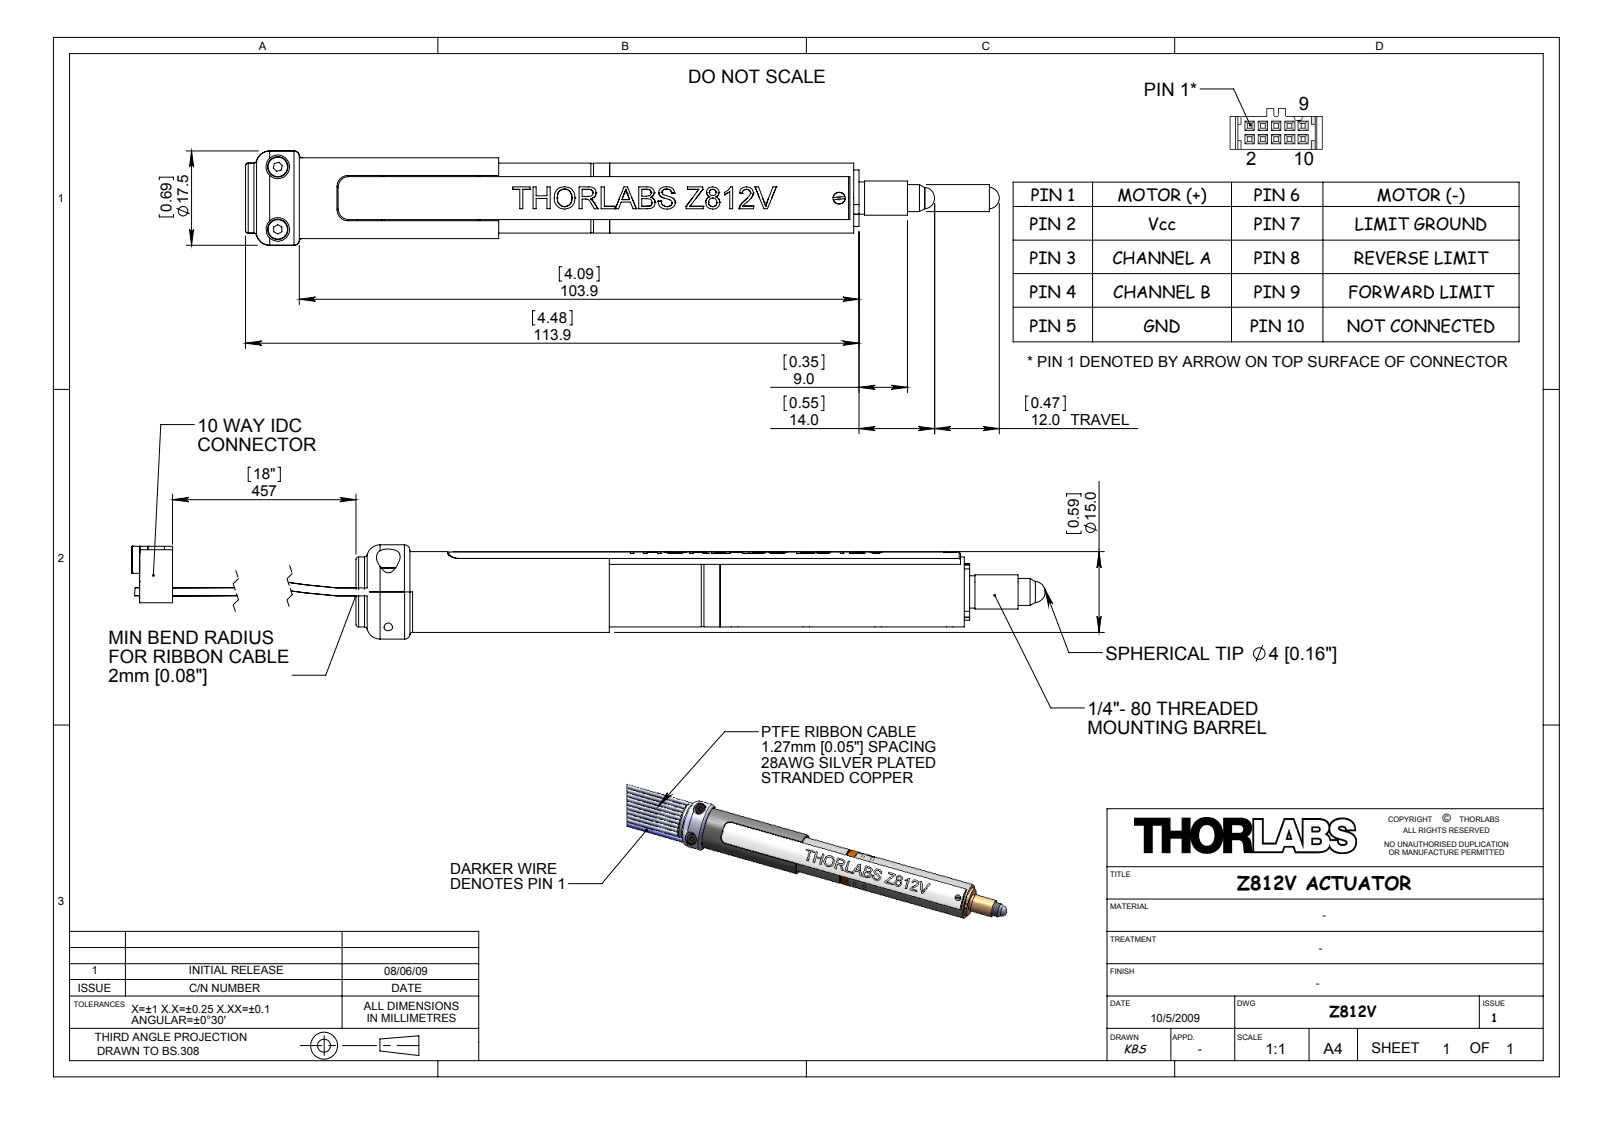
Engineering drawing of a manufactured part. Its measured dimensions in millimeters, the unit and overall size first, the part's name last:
Units: millimetres
Overall size (bounding box): 127.92 × 17.5 × 17.5
Main face-to-face distances: 7, 6.7, 48.6, 9, 10, 1, 93.9, 45.3, 112.9, 103.9
Volume: 17 617 mm³ · Surface area: 14 433 mm²
Bodies: 12 solids, 604 faces (246 planar, 0 cylindrical, 358 other)
Part name (STEP PRODUCT): Z812V
STEP written by: SolidWorks 2019 (CONFIG_CONTROL_DESIGN)
